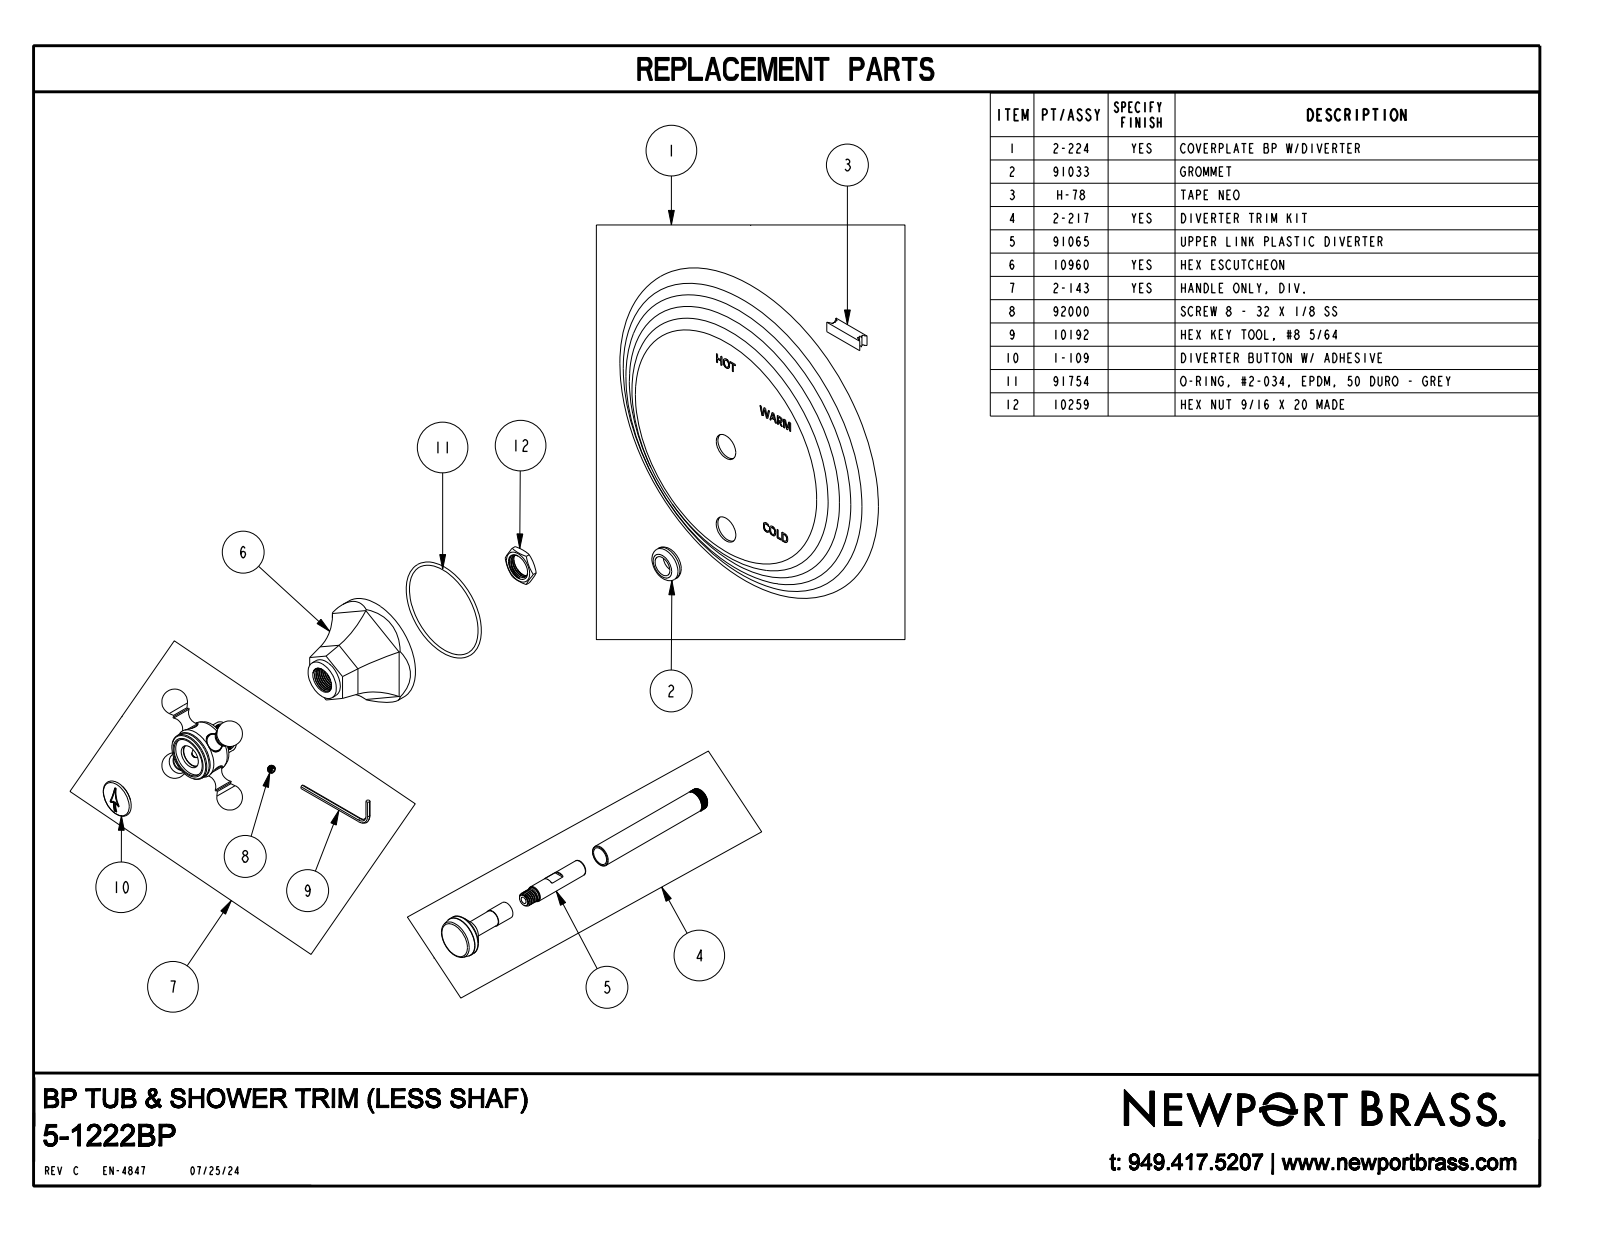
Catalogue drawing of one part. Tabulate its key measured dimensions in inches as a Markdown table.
| quantity | value |
| --- | --- |
| part name | 5-1222BP |
| STEP written by | CREO PARAMETRIC BY PTC INC, 2018400 (CONFIG_CONTROL_DESIGN) |
| units | inches |
| bodies | 1 solid, 348 faces (139 planar, 47 cylindrical, 162 other) |
| overall size | 7.75 × 7.75 × 3.616 |
| volume | 32.69 in³ |
| surface area | 120.3 in² |
| round holes (diameter × count) | 0.41 × 2, 0.855 × 1 |
| round bosses / shafts (diameter × count) | 0.392 × 2, 2.375 × 1, 1.055 × 1, 0.9 × 1, 0.86 × 1, 0.687 × 1, 0.472 × 1, 0.4 × 1 |
| partial cylindrical surfaces (radius × count) | 1.541 × 6, 0.015 × 2, 1 × 2, 1.02 × 2, 0.02 × 1 |
| main face-to-face distances | 0.754, 1.938, 1.184, 2.401, 1.647, 0.463, 2.281, 1.527, 0.343, 0.12 |
